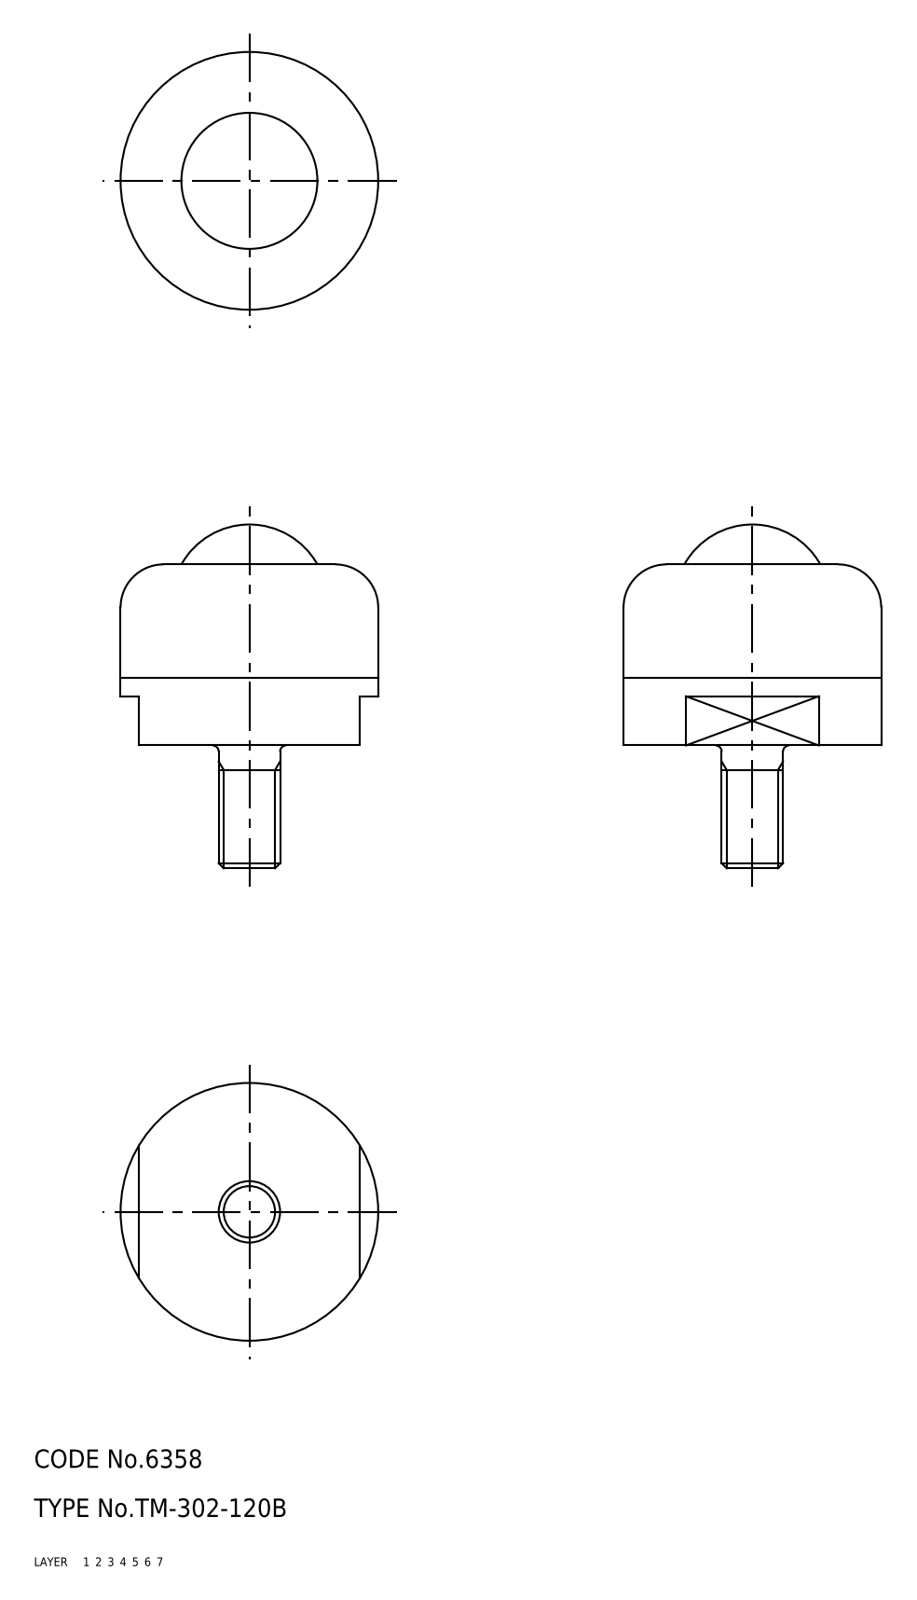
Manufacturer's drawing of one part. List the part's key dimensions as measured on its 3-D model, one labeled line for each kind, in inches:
Part name (STEP PRODUCT): 67111356; 67111369; 67111382
STEP written by: CADfix (AUTOMOTIVE_DESIGN)
Units: inches
Bodies: 3 solids, 31 faces (0 planar, 0 cylindrical, 31 other)
Overall size (bounding box): 2.205 × 1.654 × 1.654
Volume: 1.634 in³ · Surface area: 19.79 in²
